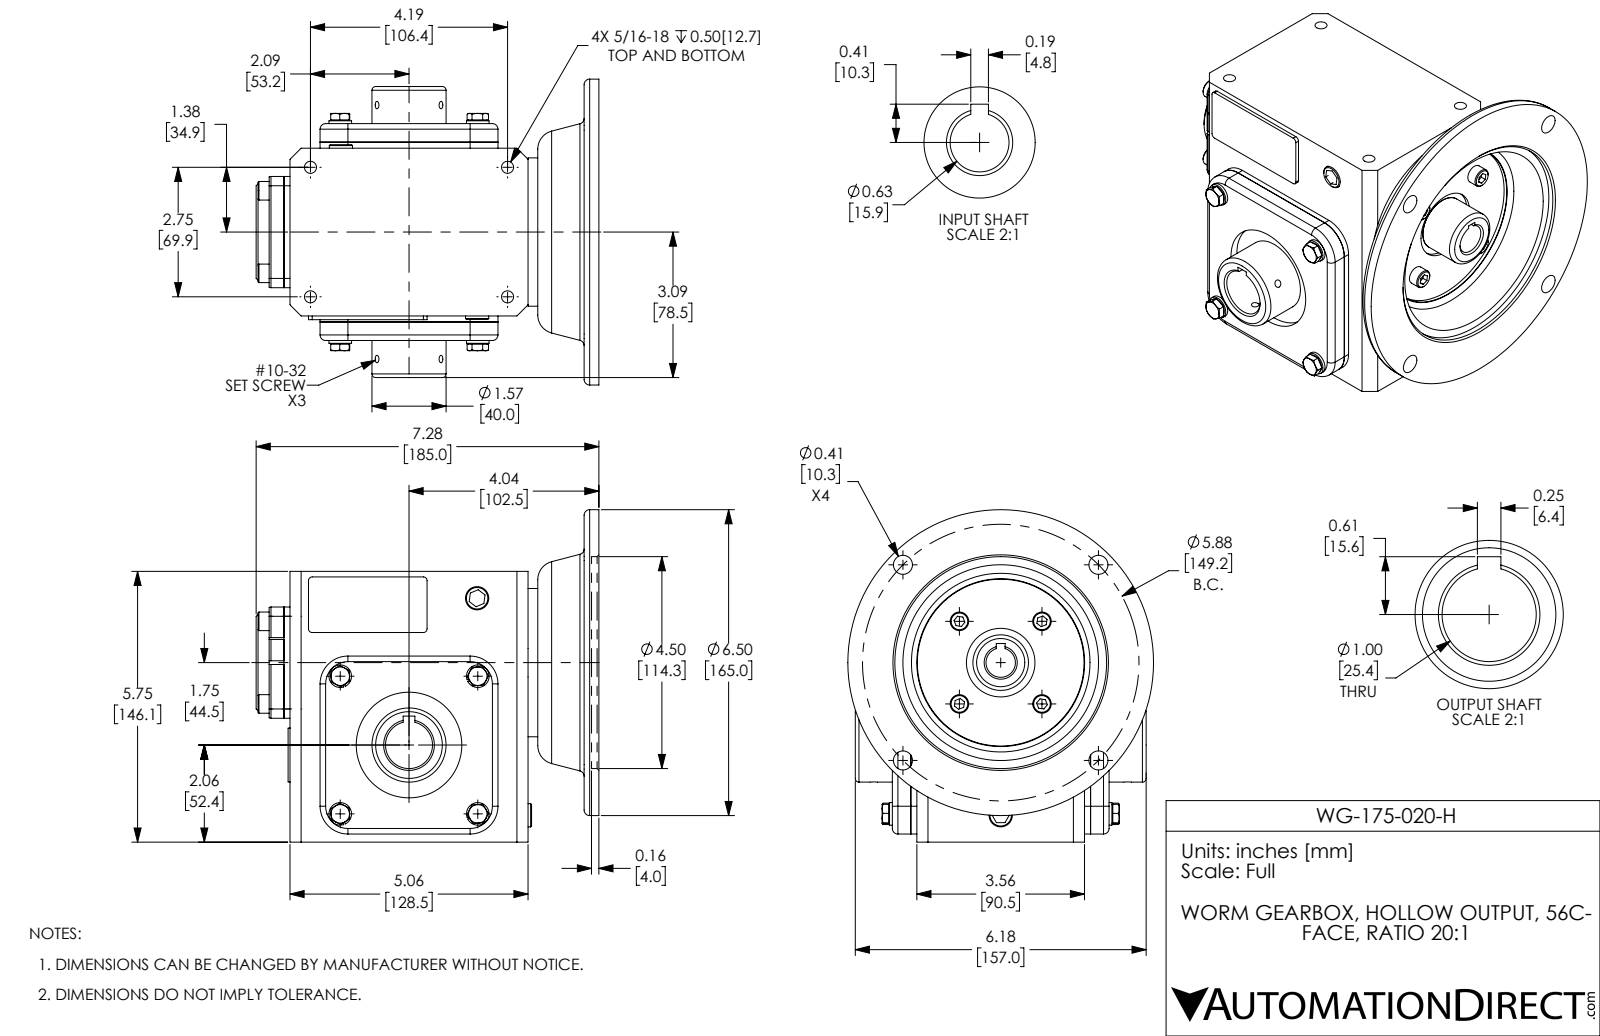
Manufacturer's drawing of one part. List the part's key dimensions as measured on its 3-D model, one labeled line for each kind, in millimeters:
Part name (STEP PRODUCT): WG-175-020-H
STEP written by: SolidWorks 2015 (CONFIG_CONTROL_DESIGN)
Units: millimetres
Bodies: 44 solids, 661 faces (339 planar, 194 cylindrical, 128 other)
Overall size (bounding box): 185 × 179.3 × 165
Volume: 2 148 000 mm³ · Surface area: 246 900 mm²
Round holes (diameter × count): ⌀4 ×6, ⌀6.5 ×4, ⌀10.3 ×4, ⌀15 ×1, ⌀15.9 ×1, ⌀25.4 ×1, ⌀37 ×1, ⌀40 ×1, ⌀57 ×1, ⌀90 ×1, ⌀114.3 ×1
Round bosses / shafts (diameter × count): ⌀10 ×8, ⌀3 ×5, ⌀12.2 ×4, ⌀165 ×1, ⌀80 ×1, ⌀52 ×1, ⌀40 ×1, ⌀30 ×1
Partial cylindrical surfaces — rounded edges, fillets, slot ends (radius × count): R2 ×8, R3 ×8, R5 ×4, R15 ×4, R0.5 ×2, R1 ×2
Main face-to-face distances: 3.3, 97, 93.8, 10, 13.3, 103.8, 107, 146.1, 8, 170
Hole centre spacings: 62.9, 74.6, 105.5, 116.3, 137, 52.8, 69.9, 106.4
